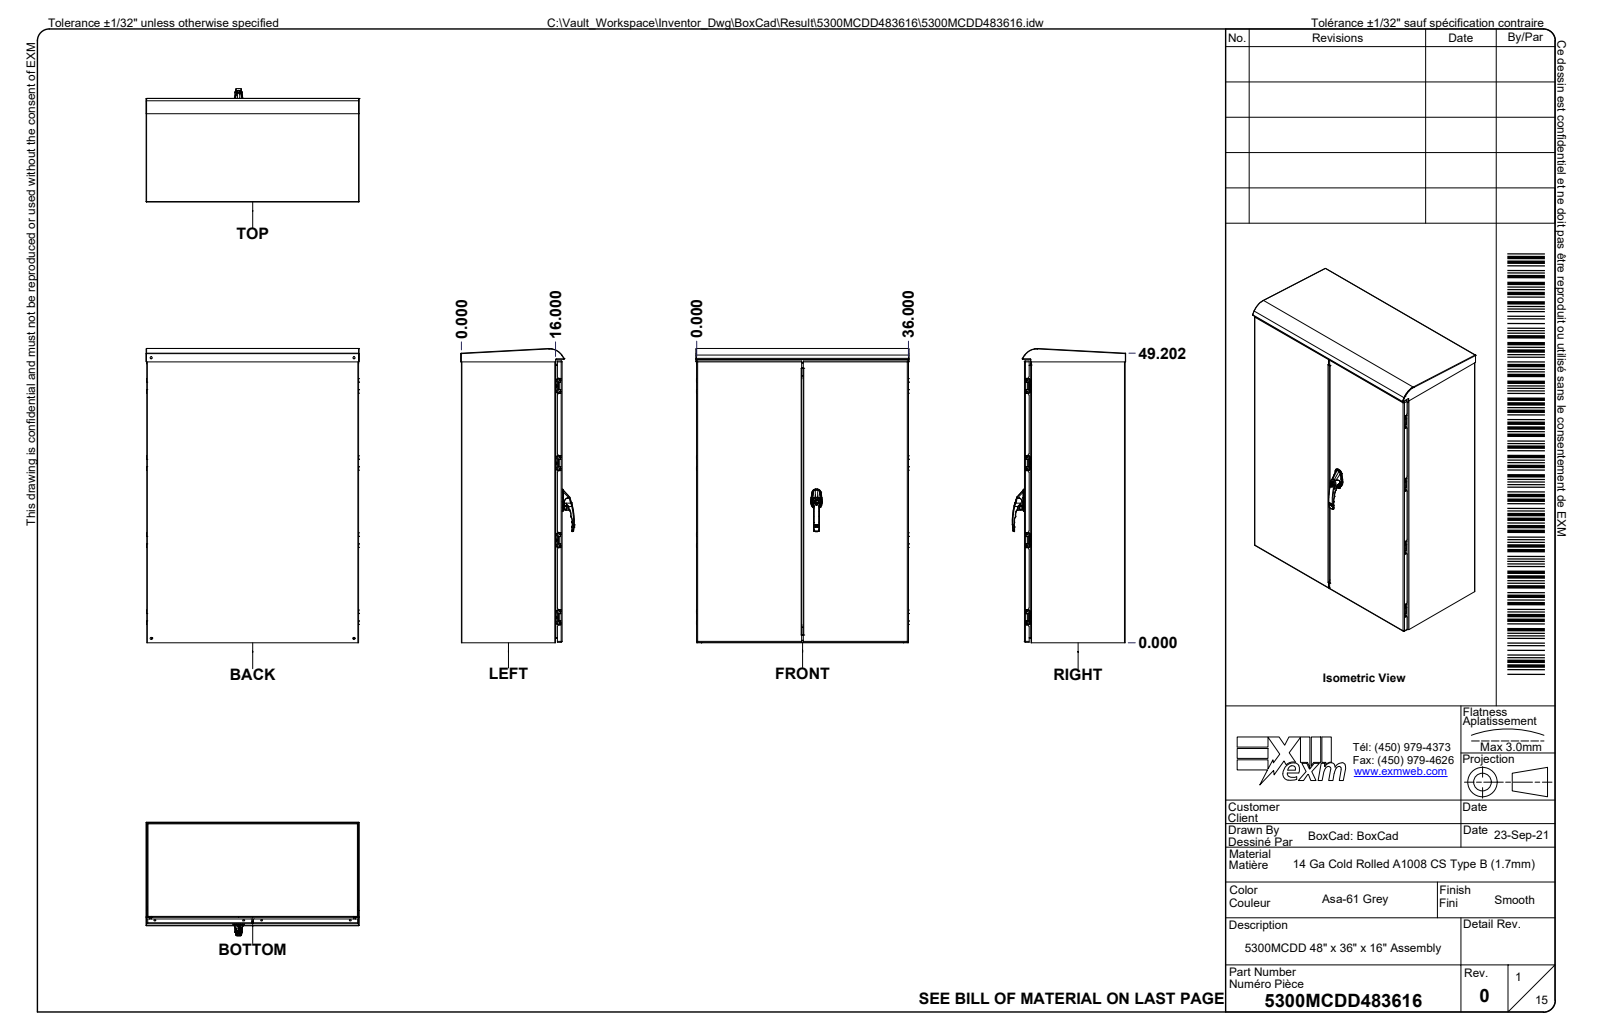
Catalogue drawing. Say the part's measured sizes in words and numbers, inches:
The part is named "5300MCDD483616; 5300MCDD483616B; 5300MCDD483616B-P; 5300MCDD483616BT-P (+8 more)". Its 3-D file was written by "Autodesk Inventor 2024 (AUTOMOTIVE_DESIGN)". It is 142 solids with 22504 faces: 6831 planar, 5570 cylindrical and 10103 other. Overall it measures 50.002 by 36.206 by 19.3 inches. Its volume is 604.4 cubic inches and its surface area 17 758 square inches. Round holes: 24 of diameter 0.043, 24 of diameter 0.29, 14 of diameter 0.03, 10 of diameter 0.167, 10 of diameter 0.315, 10 of diameter 0.5, 8 of diameter 0.178, 8 of diameter 0.27, 6 of diameter 0.201, 6 of diameter 0.305, 4 of diameter 0.22, 4 of diameter 0.33. Round bosses or shafts: 24 of diameter 0.039, 13 of diameter 0.03, 8 of diameter 0.717, 8 of diameter 0.311, 8 of diameter 0.262, 8 of diameter 0.232, 6 of diameter 0.472, 6 of diameter 0.3. Partial cylindrical surfaces (rounded edges, fillets, slot ends): 419 of radius 0.02, 359 of radius 0.01, 338 of radius 0.039, 253 of radius 0.008, 119 of radius 0.016, 118 of radius 0.004, 83 of radius 0.079, 72 of radius 0.031. The main face-to-face distances are 0.068, 17.052, 16.983, 17.12, 35.932, 0.068, 0.874, 0.942, 16.109, 16.178. The hole center spacings are 48.246, 47.95, 49.122, 13.101, 26.202, 1.052, 5.333, 10.667.
